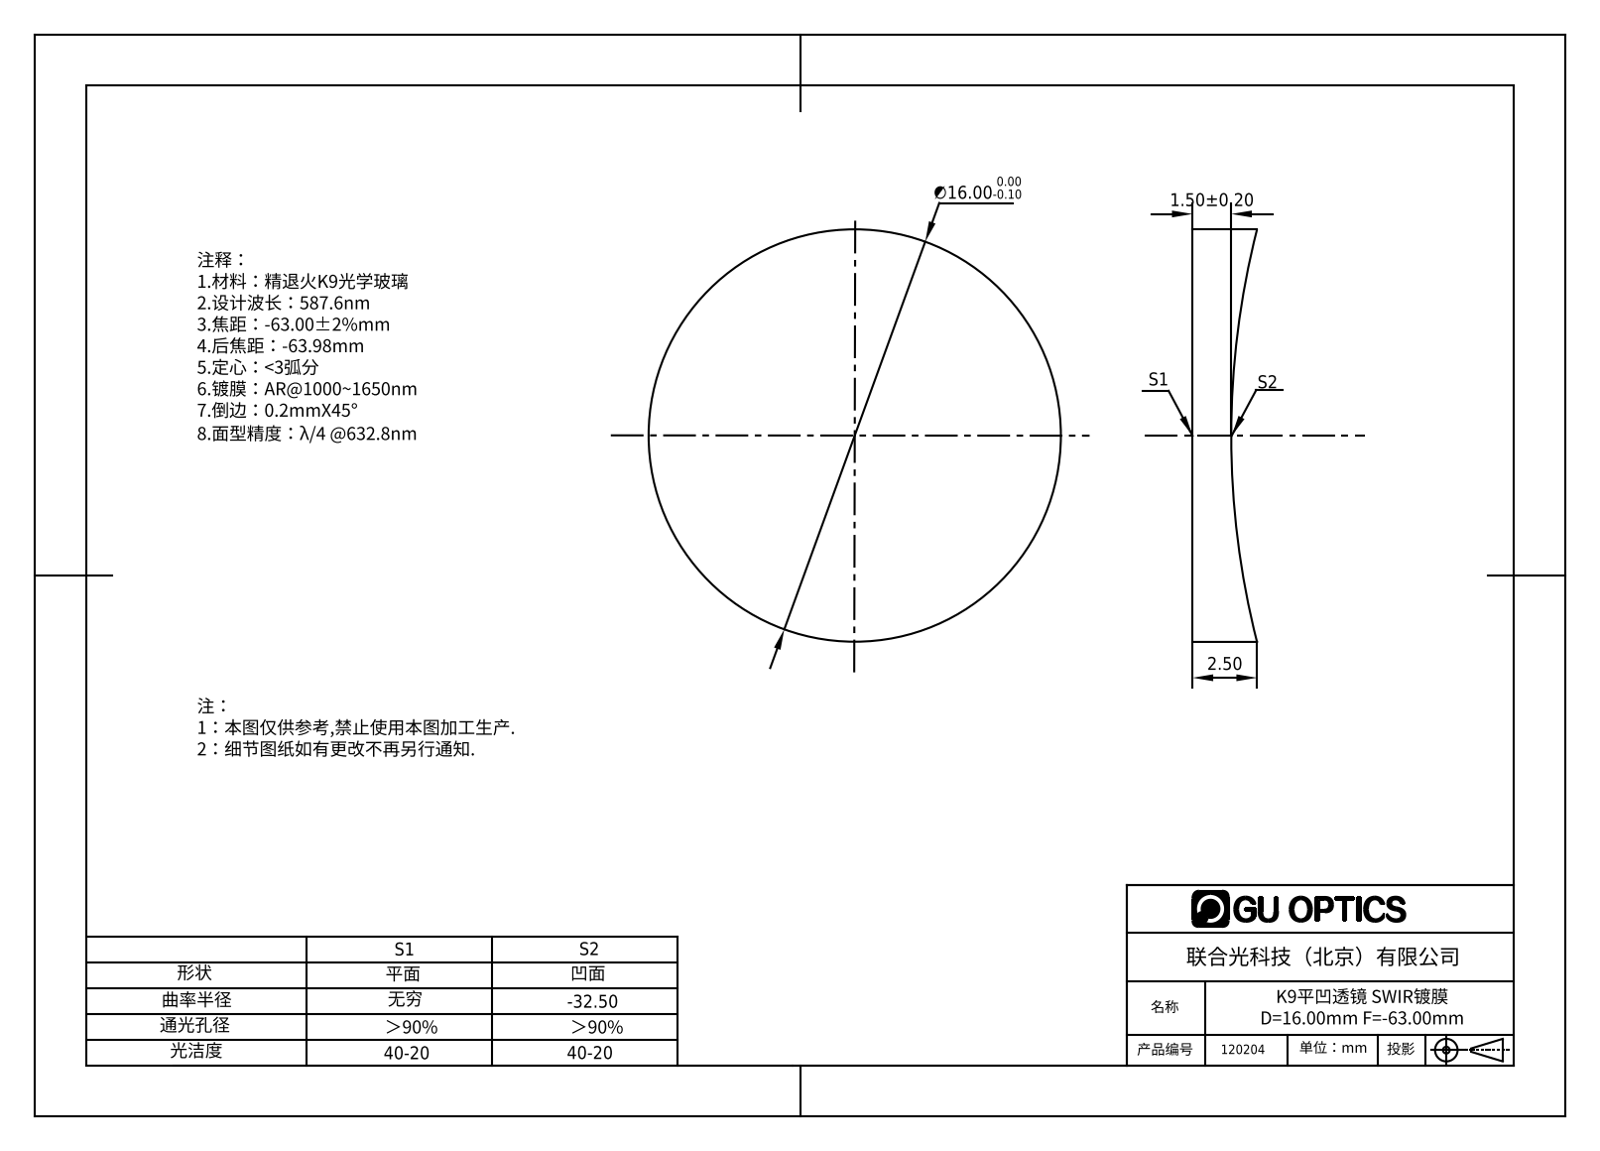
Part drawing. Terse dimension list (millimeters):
name: 120144
written by: SolidWorks 2016 (AUTOMOTIVE_DESIGN)
unit: mm
bodies: 1 solid, 5 faces (1 planar, 2 cylindrical, 2 other)
size: 16 × 16 × 2.5
volume: 402 mm³; area: 531 mm²
bosses: 1× ⌀16
